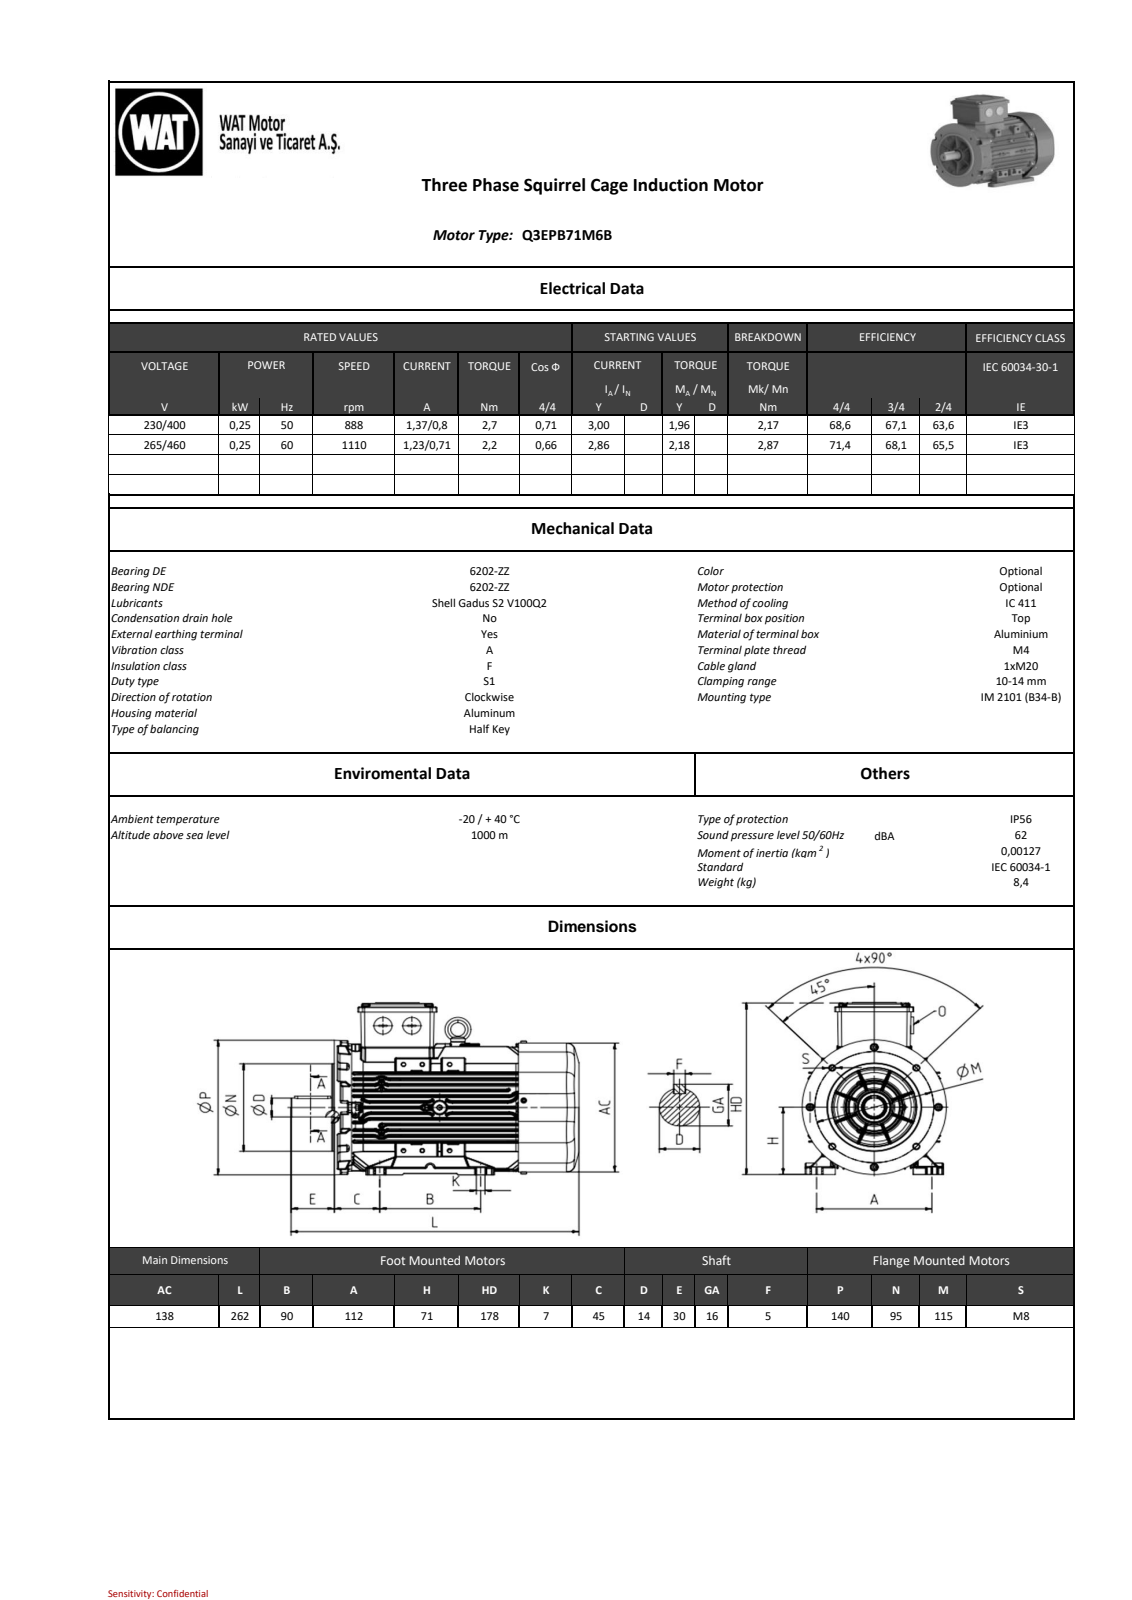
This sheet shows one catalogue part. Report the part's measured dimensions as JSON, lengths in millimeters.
{"part_name": "001_objects", "step_written_by": "SIEMENS PLM Software NX2206.8101 (AUTOMOTIVE_DESIGN)", "units": "millimeters", "bodies": {"solids": 0, "faces": 2859, "planar": 1423, "cylindrical": 765, "other": 671}, "overall_size": [262, 178.11, 140.48], "round_holes": [[3.65, 8], [4, 8], [2.5, 6], [3.3, 5], [5, 5], [8, 5], [4.5, 4], [4.65, 4], [4.8, 4], [5.2, 4], [7, 4], [3, 3]], "round_bosses_or_shafts": [[8, 8], [4, 8], [3.3, 4], [140.48, 1], [138, 1], [115, 1], [95, 1], [61, 1]], "partial_cylinders_radius": [[1, 109], [0.5, 54], [2, 39], [1.2, 36], [1.5, 24], [4, 17], [5, 17], [10, 16]], "face_to_face_distances": [2, 3, 5, 1, 197.5, 15, 194.5, 83, 35, 6.9], "hole_center_spacings": [61.39, 84.39, 84.47, 87.43, 55, 36.59, 67.18, 67.2]}
